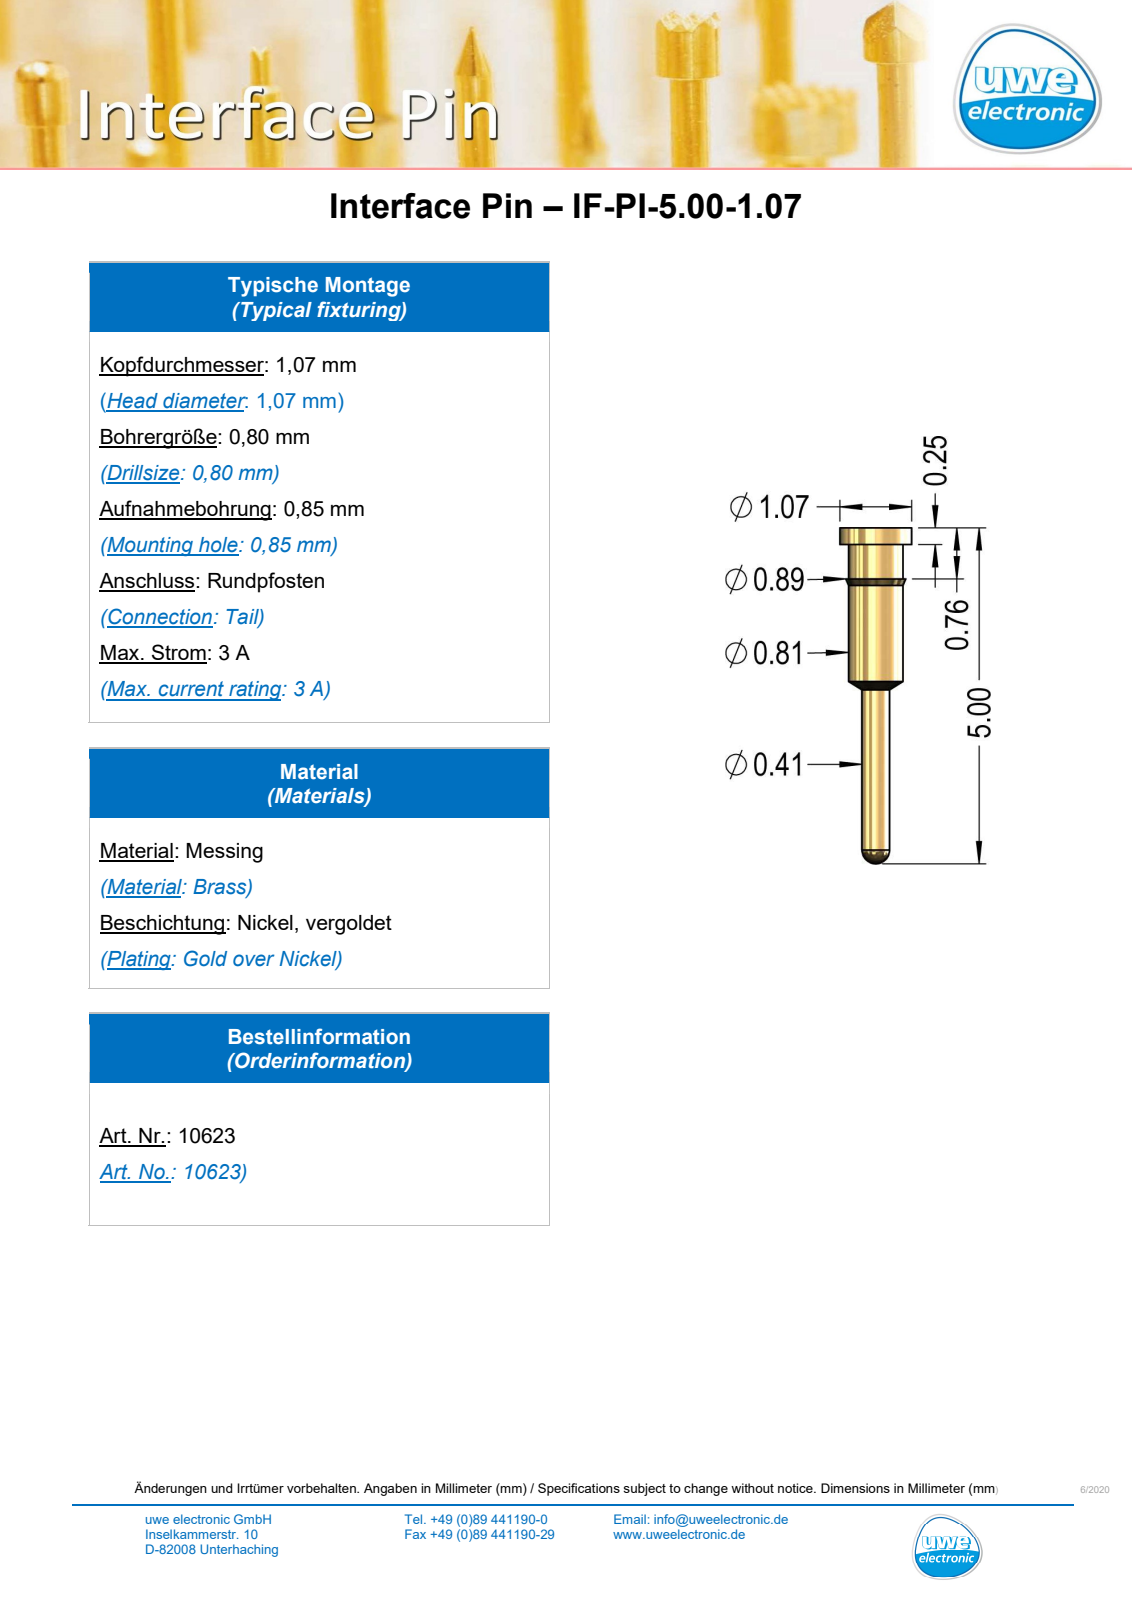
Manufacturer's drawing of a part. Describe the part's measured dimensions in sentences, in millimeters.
The part is named "IF-PI-5.00-1.07". Its 3-D file was written by "SolidWorks 2020 (AUTOMOTIVE_DESIGN)". It is 1 solid with 17 faces: 3 planar, 8 cylindrical and 6 other. Overall it measures 5 by 1.07 by 1.07 millimeters. Its volume is 2 cubic millimeters and its surface area 11 square millimeters. Round bosses or shafts: 1 of diameter 1.07, 1 of diameter 0.81, 1 of diameter 0.41. The main face-to-face distances are 0.51, 0.76.
